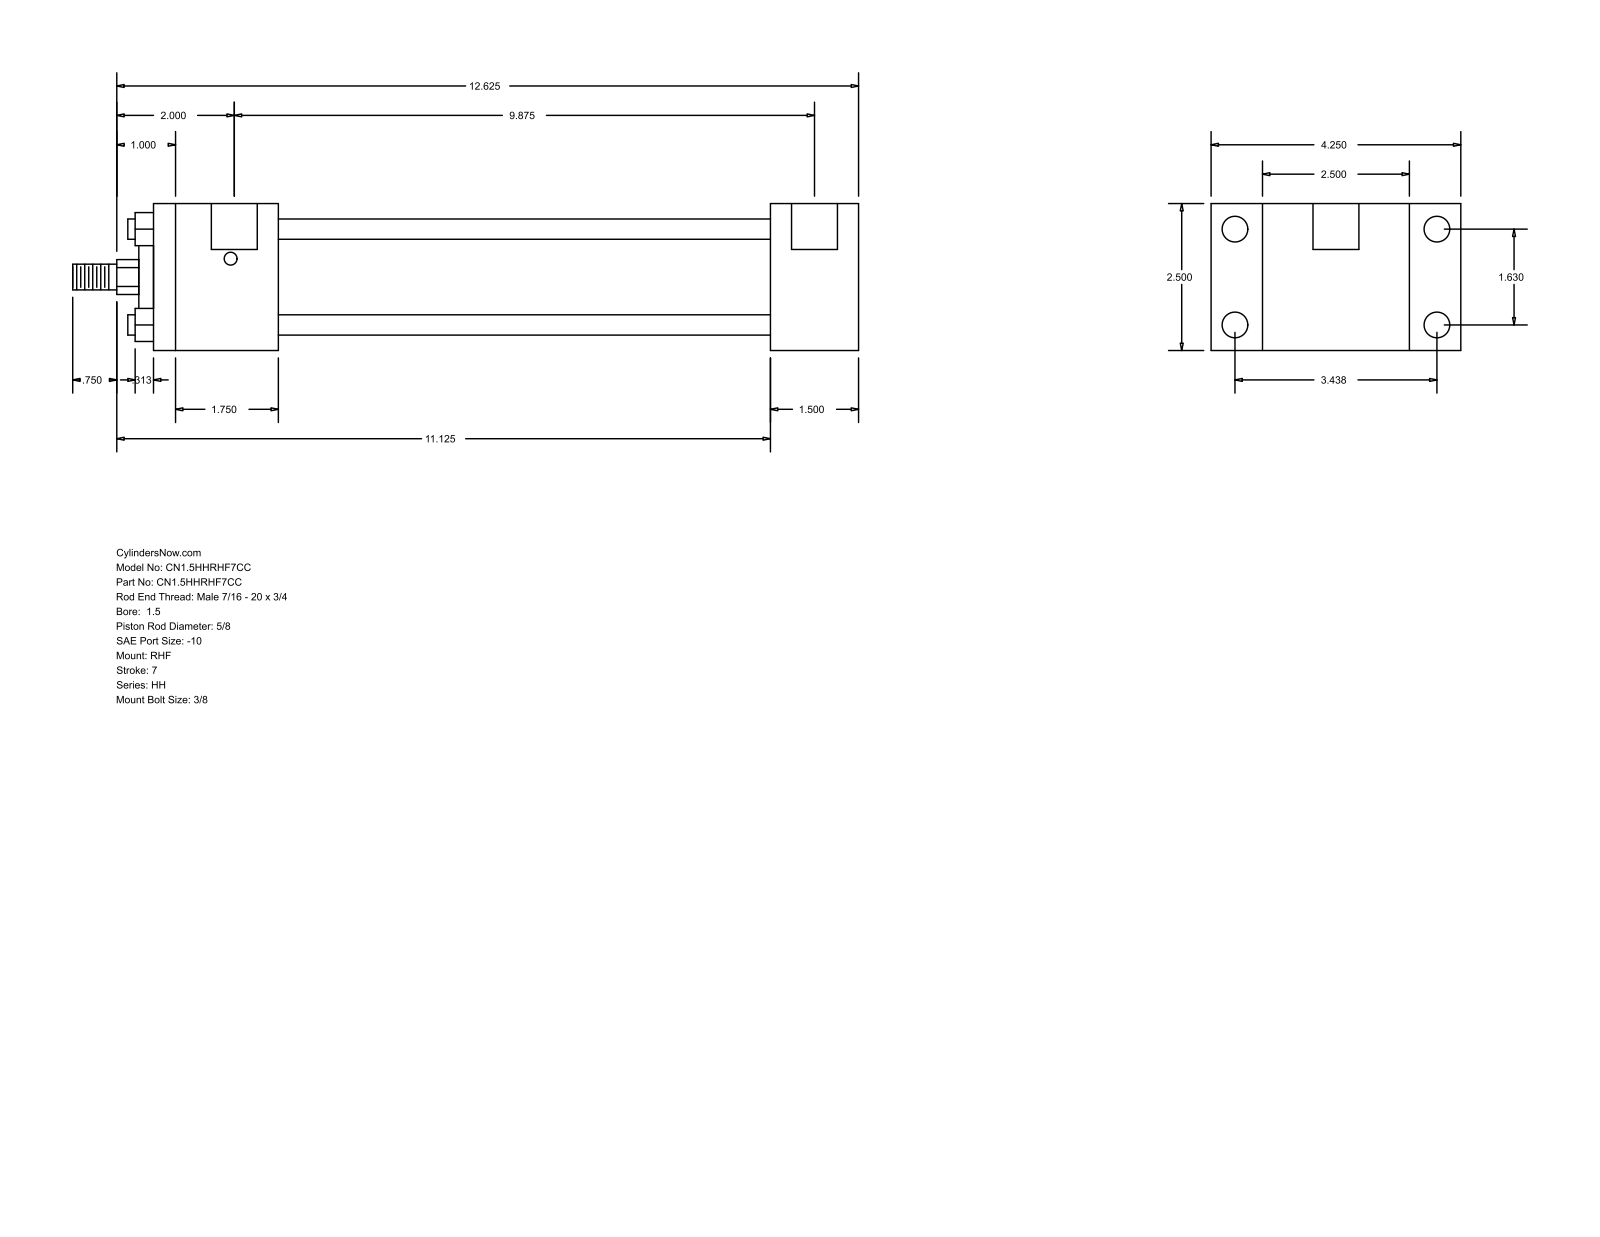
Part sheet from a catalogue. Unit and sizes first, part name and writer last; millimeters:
Units: millimetres
Overall size (bounding box): 339.73 × 107.95 × 63.5
Round holes (diameter × count): ⌀5.56 ×4, ⌀11.13 ×4, ⌀19.84 ×2
Round bosses / shafts (diameter × count): ⌀8.76 ×4, ⌀44.45 ×1, ⌀28.57 ×1, ⌀15.88 ×1, ⌀11.11 ×1
Partial cylindrical surfaces — rounded edges, fillets, slot ends (radius × count): R7.54 ×1
Main face-to-face distances: 63.5, 22.23, 85.73, 38.11, 266.69, 304.8, 107.96, 53.97, 212.72, 250.83
Hole centre spacings: 1.59, 41.4, 87.32, 96.64, 252.41, 254, 250.82
Bodies: 0 solids, 88 faces (60 planar, 28 cylindrical, 0 other)
Part name (STEP PRODUCT): HH_RHF__0150_0.625
STEP written by: GSSL Pune (CONFIG_CONTROL_DESIGN)
